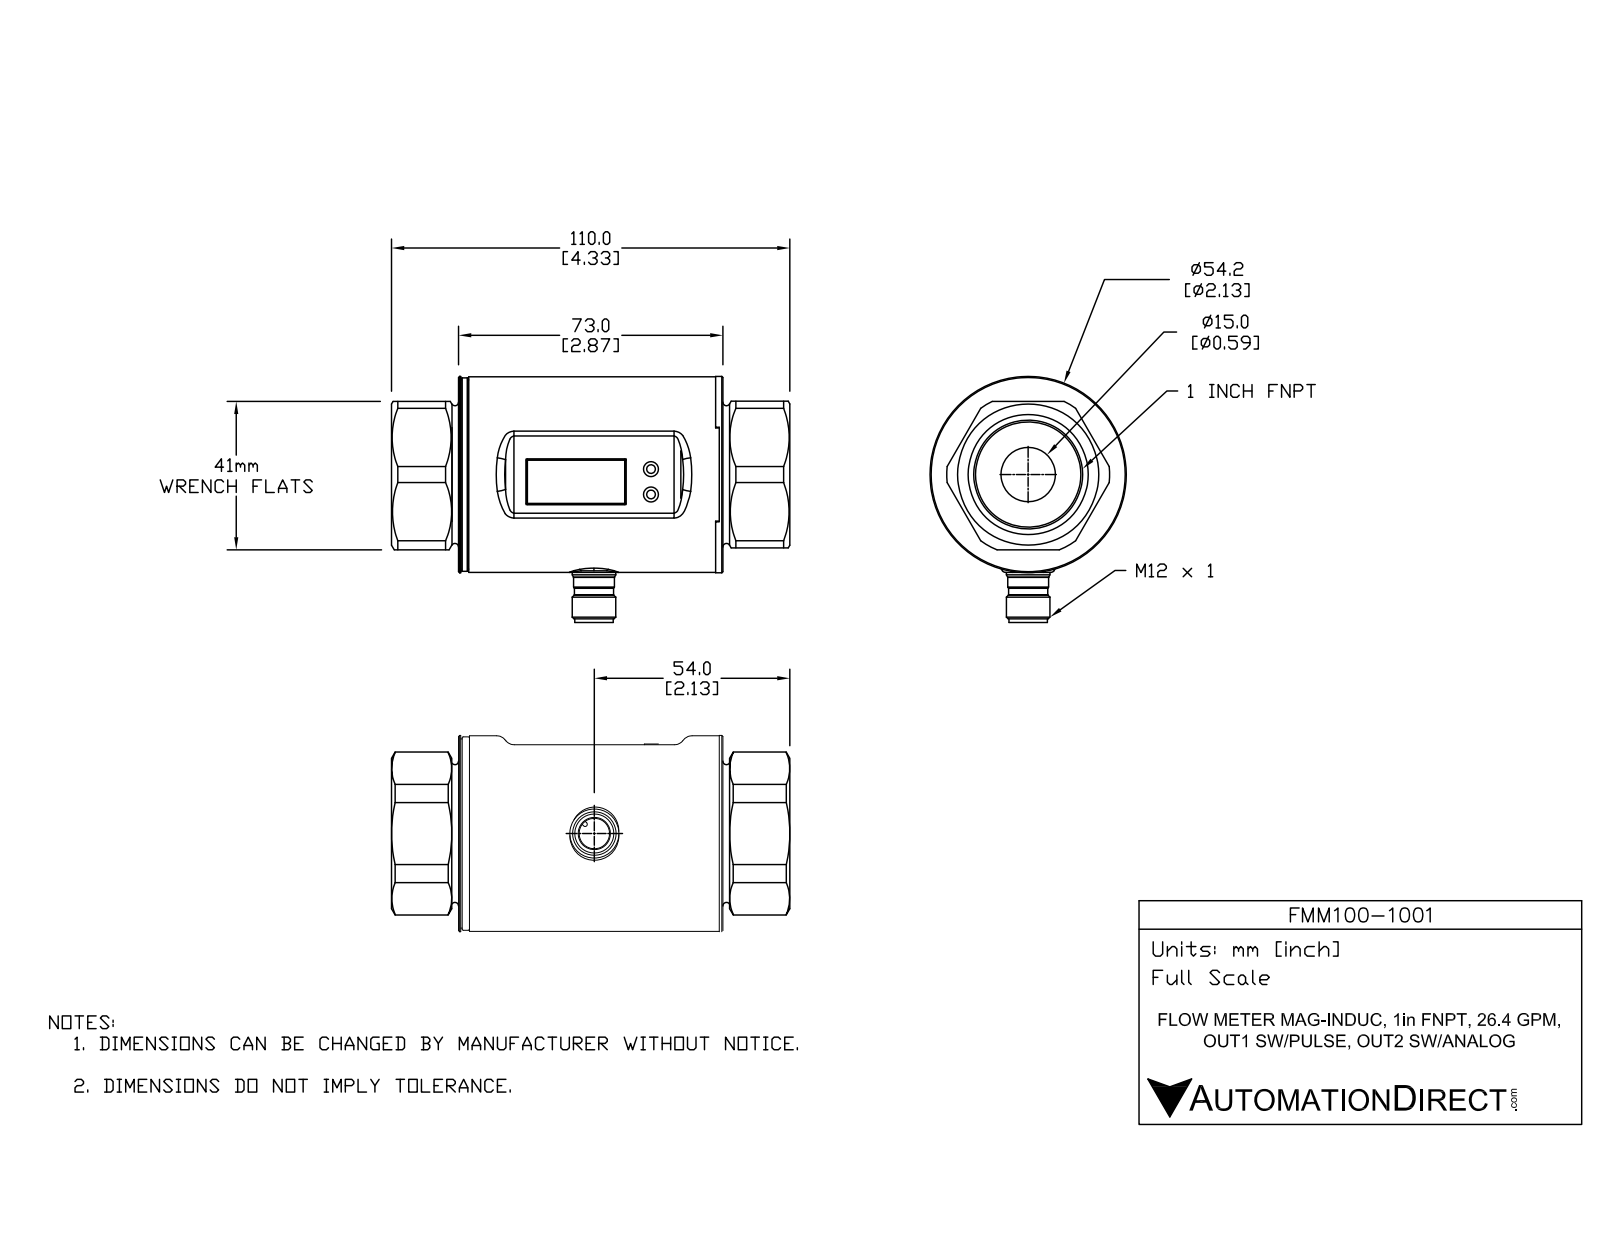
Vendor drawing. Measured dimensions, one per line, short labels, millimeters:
name: FMM100-1001
written by: SolidWorks 2015 (AUTOMOTIVE_DESIGN)
unit: mm
bodies: 11 solids, 214 faces (84 planar, 85 cylindrical, 45 other)
size: 109.99 × 67.85 × 54.2
volume: 62 314 mm³; area: 62 669 mm²
holes: 2× ⌀1.5, 2× ⌀3.6, 2× ⌀4.11, 1× ⌀8.4, 1× ⌀12, 1× ⌀15, 1× ⌀30, 1× ⌀52
bosses: 2× ⌀3.9, 1× ⌀54.2, 1× ⌀54, 1× ⌀53.4, 1× ⌀52.2, 1× ⌀40, 1× ⌀12, 1× ⌀11.3
rounds: 4× R1, 2× R0.3, 2× R2, 2× R3, 1× R0.6, 1× R22.5
face distances: 70, 2, 1, 5, 68, 71.7, 72, 72.7, 73, 1.87
hole spacings: 13, 1.25, 7, 8, 9.25, 21, 22.25, 26
